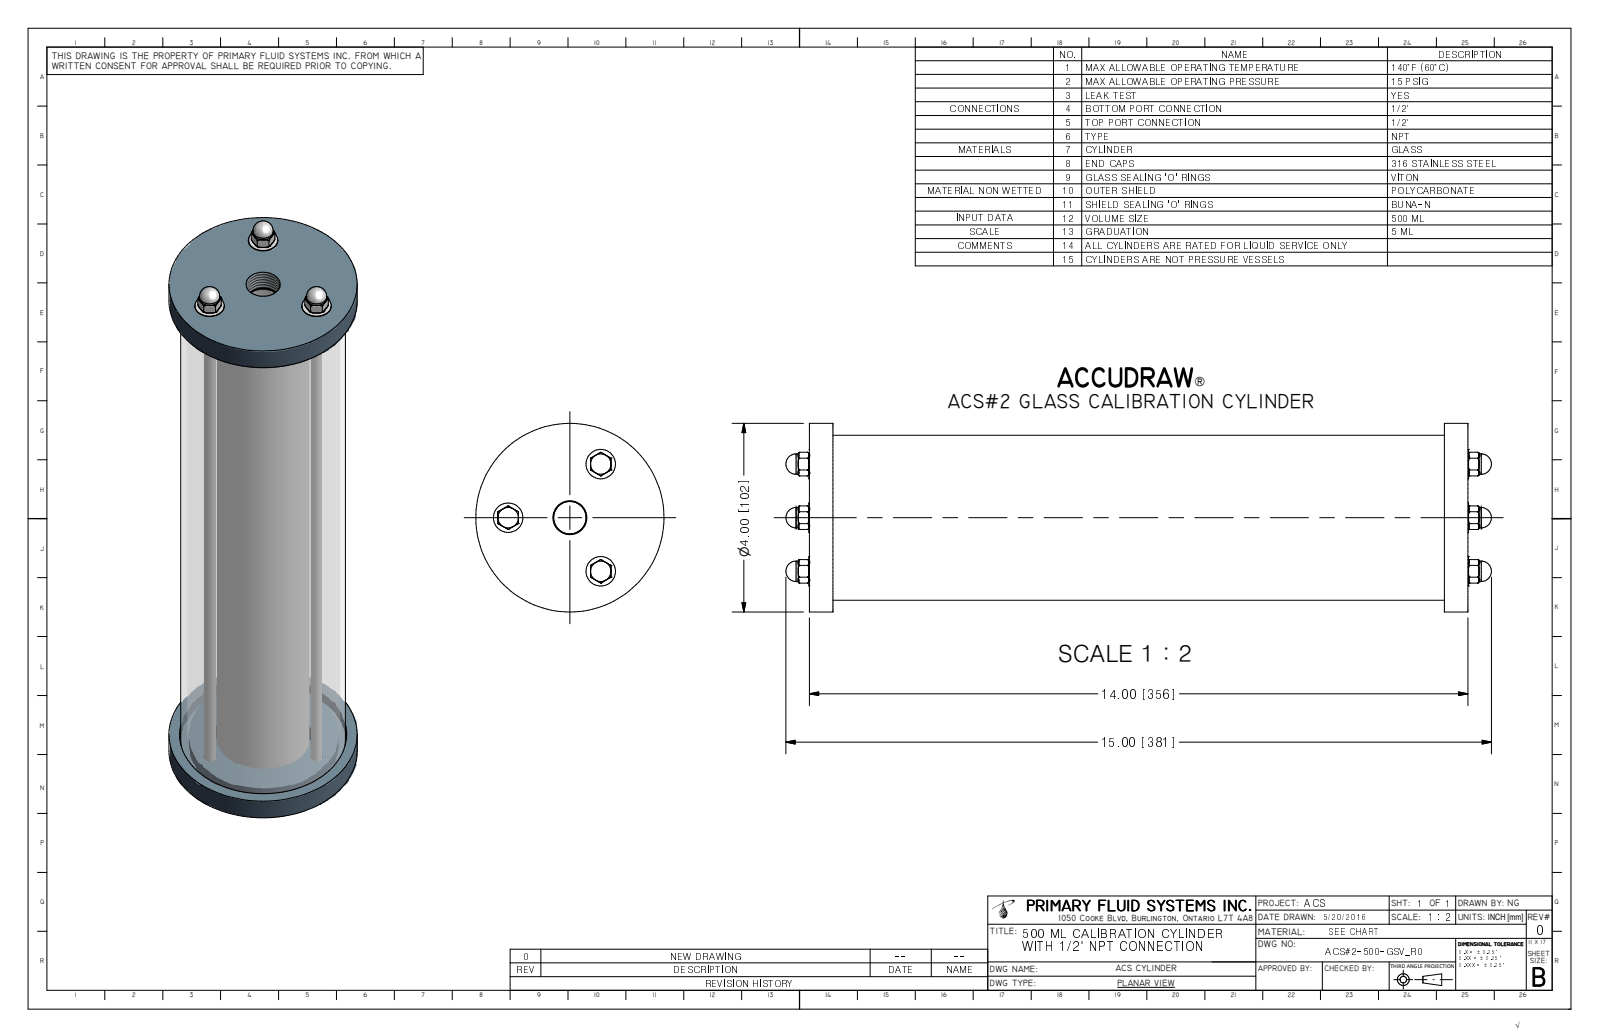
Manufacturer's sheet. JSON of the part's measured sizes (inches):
{"part_name": "ACS#2-500-GSV_R0; ACS-3-500-METAL_R3; ACS-2-500-PC_R6; ACS-1-500-A_R0 (+3 more)", "step_written_by": "Autodesk Inventor 2009 (AUTOMOTIVE_DESIGN)", "units": "inches", "bodies": {"solids": 19, "faces": 429, "planar": 38, "cylindrical": 41, "other": 350}, "overall_size": [15, 4, 4], "volume_in3": 36.41, "surface_area_in2": 572.5, "round_holes": [[0.18, 3], [0.266, 3], [0.281, 3], [1.811, 1], [2.05, 1], [3.25, 1], [3.55, 1]], "round_bosses_or_shafts": [[0.625, 3], [0.25, 3], [4, 1], [3.5, 1], [3.2, 1], [1.969, 1], [1.7, 1]], "face_to_face_distances": [0.5, 13.5, 14, 13, 0.225, 13.775, 0.275, 13.275, 0.1, 0.125], "hole_center_spacings": [1.313, 2.273]}
